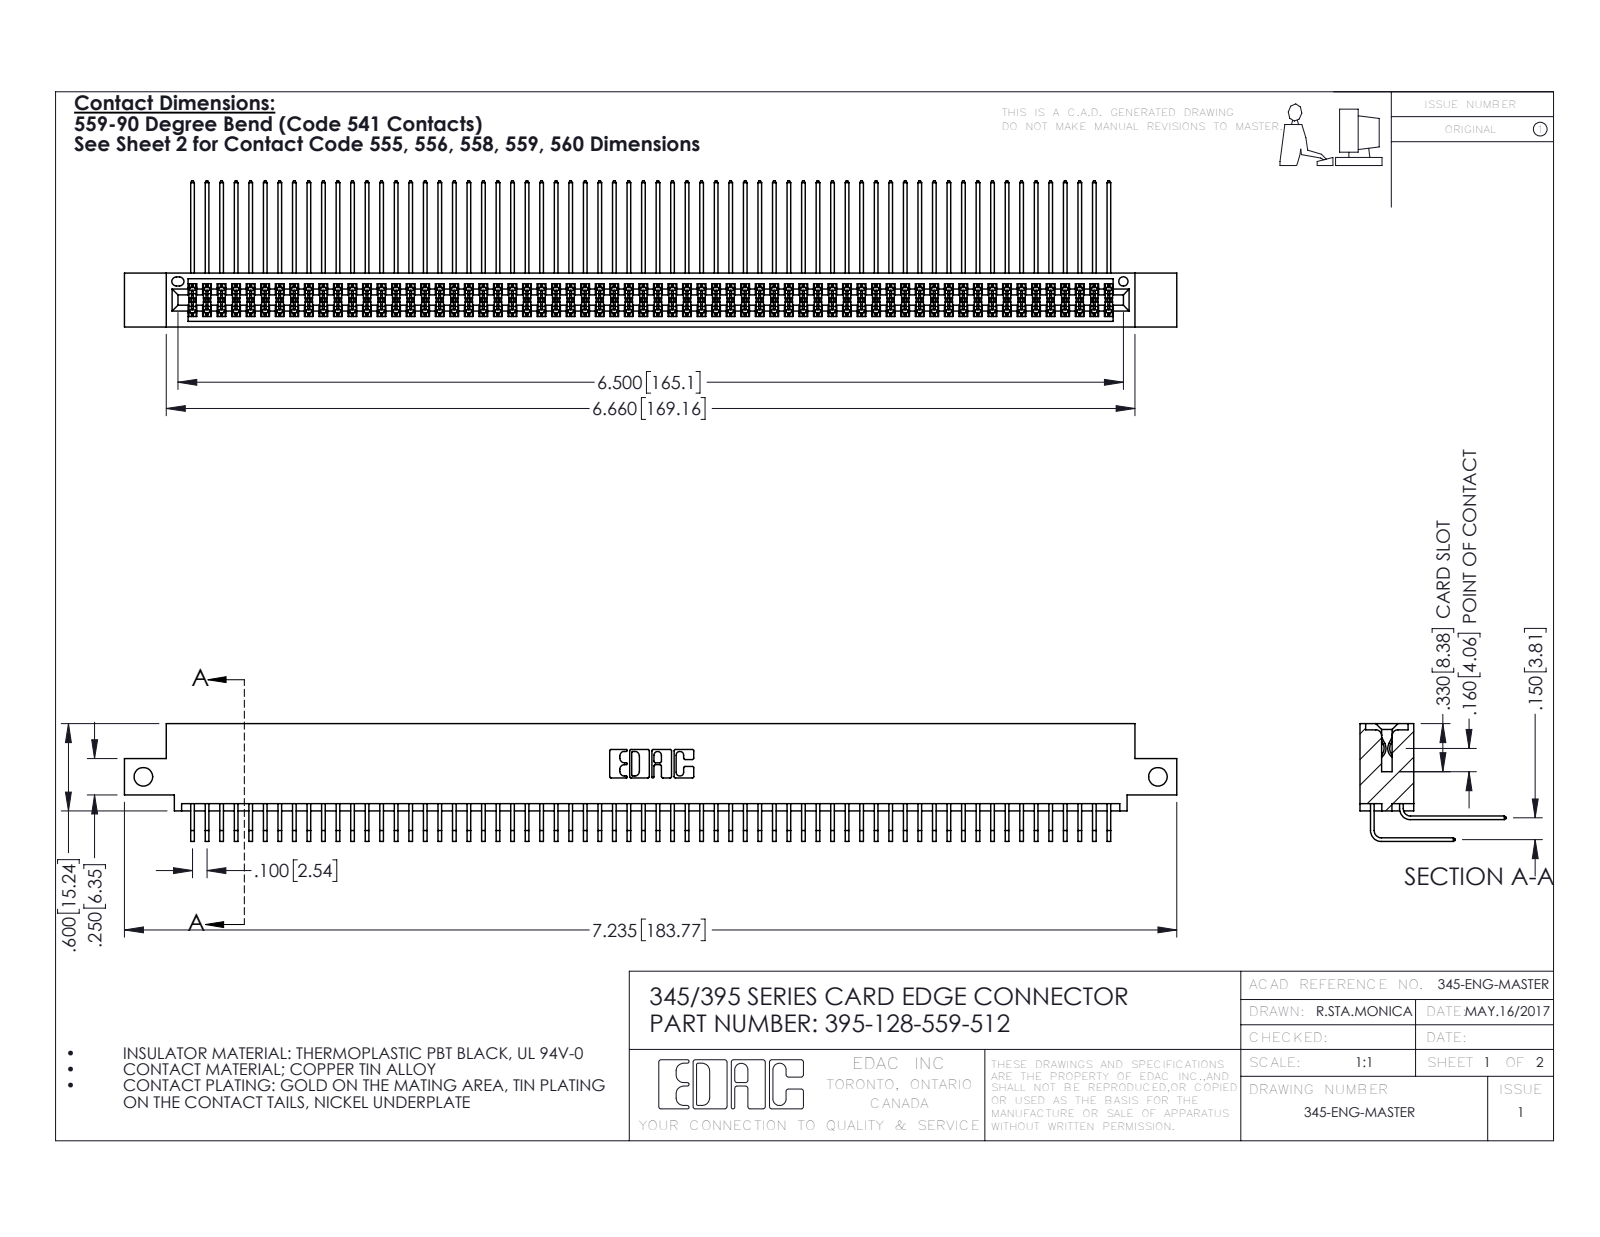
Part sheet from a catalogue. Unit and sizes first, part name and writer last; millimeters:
Units: millimetres
Overall size (bounding box): 183.8 × 25.5 × 20.5
Round holes (diameter × count): ⌀3.3 ×2, ⌀1.6 ×1
Partial cylindrical surfaces — rounded edges, fillets, slot ends (radius × count): R0.2 ×193, R0.3 ×22, R0.2 ×6, R0.8 ×6, R0.7 ×3, R0.4 ×2, R0.5 ×2, R0.6 ×2
Main face-to-face distances: 1.8, 7.6, 5.1, 9.4, 2.5, 6.9, 0.6, 5.7, 4.4, 3.8
Hole centre spacings: 177.2
Volume: 18 630 mm³ · Surface area: 31 400 mm²
Bodies: 129 solids, 6786 faces (4564 planar, 2222 cylindrical, 0 other)
Part name (STEP PRODUCT): 395-128-559-512; 345 Part_0.110 Offset - Side Mount; 345-292-001_558 559 Tail - 1; 345-292-001_559 Tail - 2
STEP written by: SolidWorks 2016 (CONFIG_CONTROL_DESIGN)
